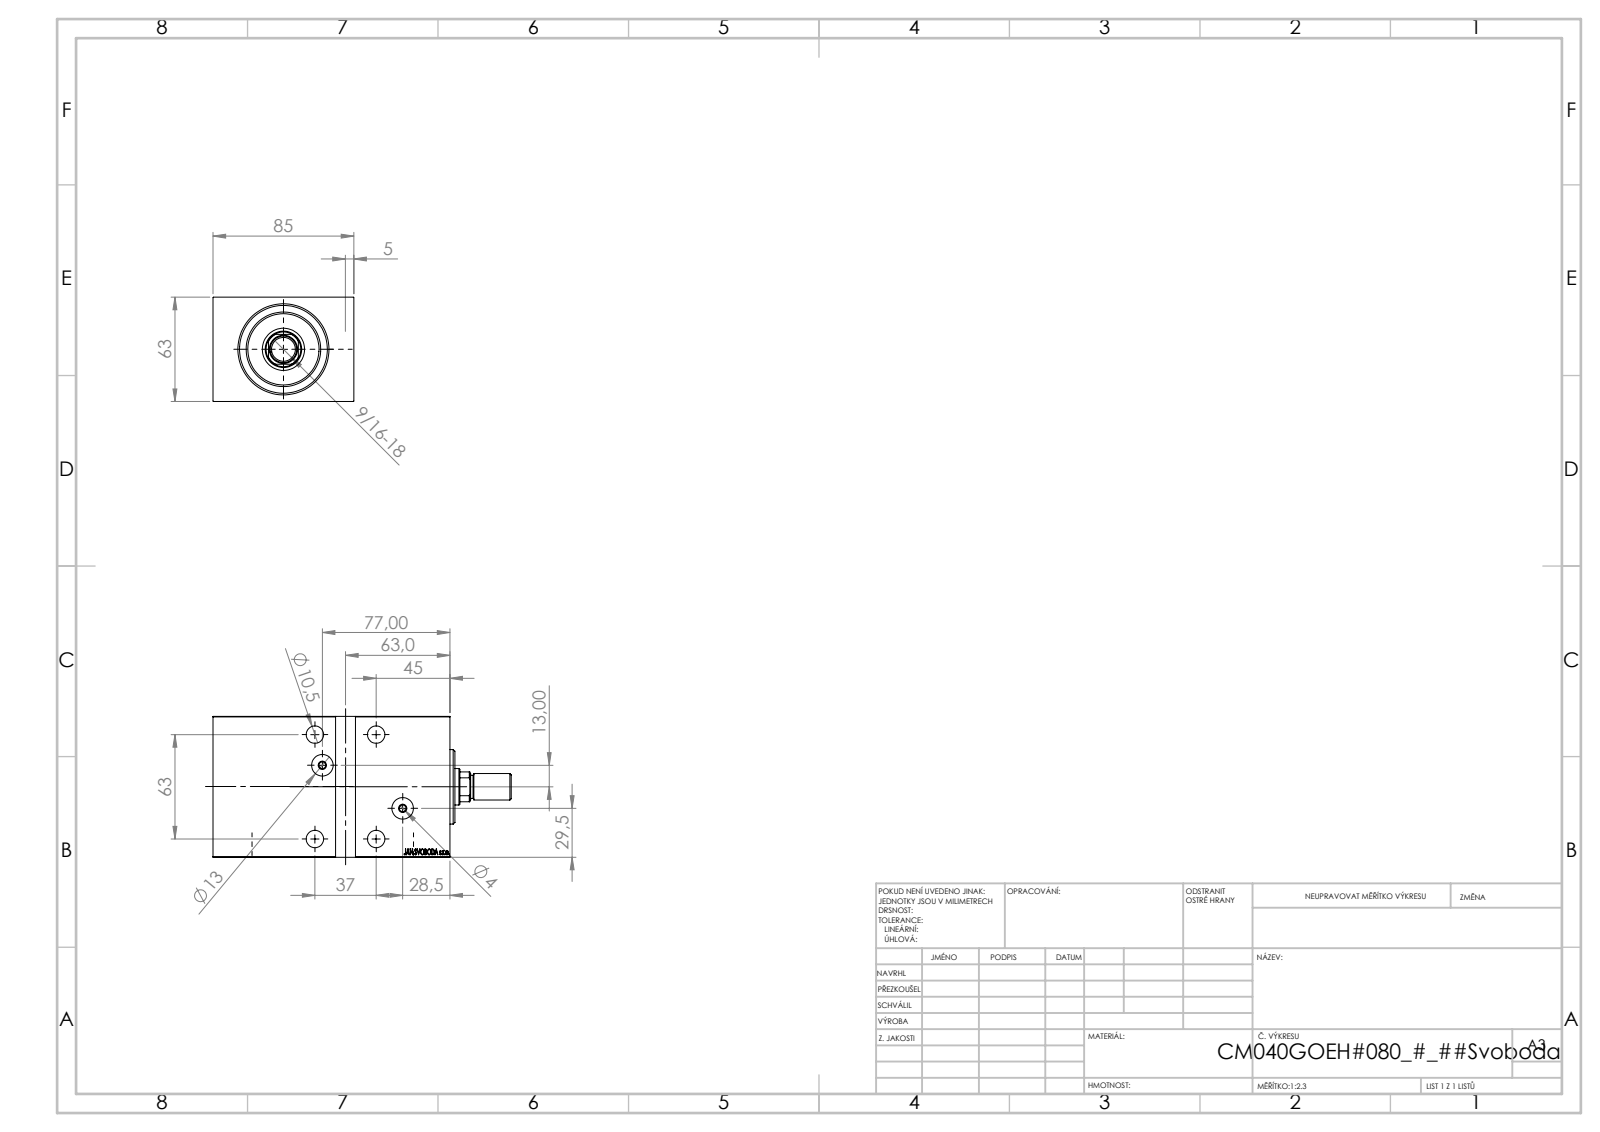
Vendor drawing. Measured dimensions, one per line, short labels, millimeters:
name: V450CM_MALE_METRIC; V450CM_VC_G; V450CM_G_VCP; Zatka_OIL_PORT (+1 more)
written by: SolidWorks 2019 (CONFIG_CONTROL_DESIGN)
unit: mm
bodies: 6 solids, 913 faces (447 planar, 62 cylindrical, 404 other)
size: 180 × 85 × 63
volume: 668 404 mm³; area: 104 350 mm²
holes: 4× ⌀10.5, 4× ⌀16.5, 2× ⌀4, 2× ⌀13, 1× ⌀12.5, 1× ⌀22, 1× ⌀25.5, 1× ⌀40, 1× ⌀42, 1× ⌀53
bosses: 2× ⌀18, 2× ⌀5, 1× ⌀45, 1× ⌀27, 1× ⌀16, 1× ⌀14
rounds: 1× R10.5
face distances: 63, 85, 143, 12, 131, 5, 138, 126, 3, 60
hole spacings: 37, 63, 73.06, 19.04, 24.46, 37.4, 44.73, 47.29
